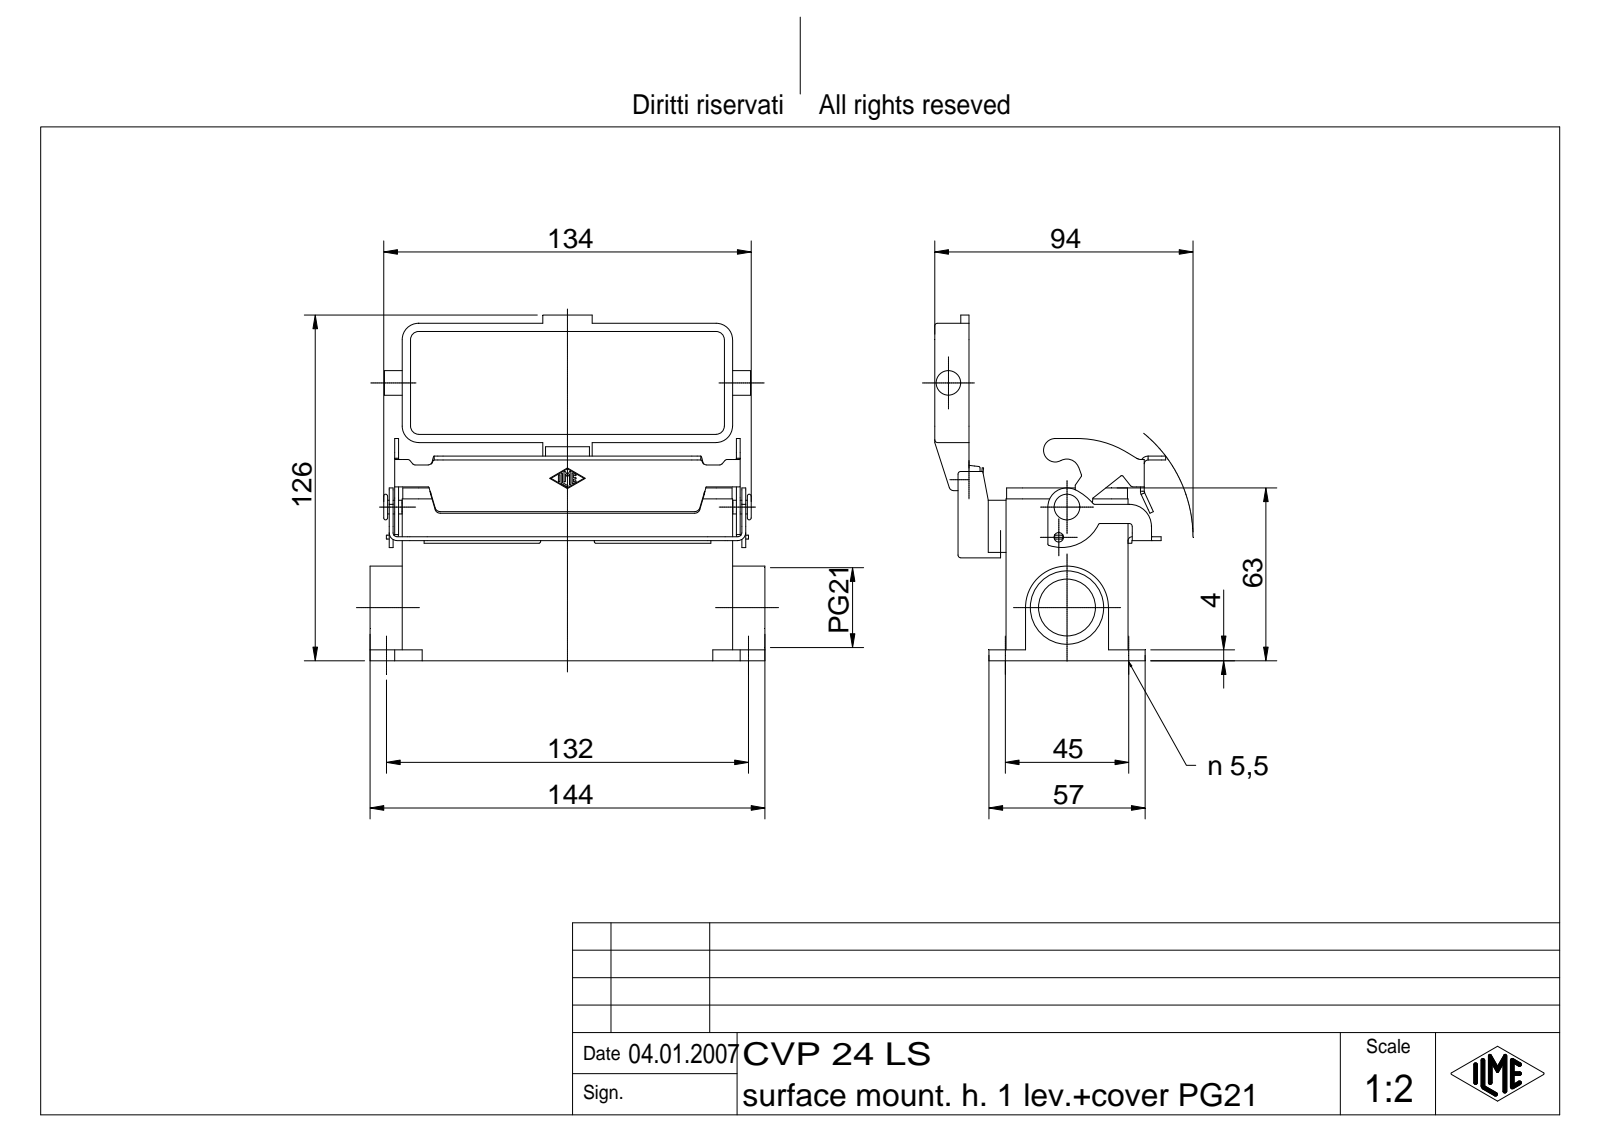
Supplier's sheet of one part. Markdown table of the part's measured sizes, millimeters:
| quantity | value |
| --- | --- |
| part name | CVP 24 LS |
| STEP written by | Autodesk Inventor 7 (AUTOMOTIVE_DESIGN) |
| units | millimeters |
| bodies | 4 solids, 572 faces (222 planar, 185 cylindrical, 165 other) |
| overall size | 144 × 126 × 84.23 |
| volume | 160 346 mm³ |
| surface area | 93 832 mm² |
| round holes (diameter × count) | 5.5 × 4, 3.5 × 1, 4 × 1, 20.78 × 1, 26.78 × 1 |
| round bosses / shafts (diameter × count) | 5 × 2, 9 × 1, 7 × 1, 3.2 × 1, 3 × 1 |
| partial cylindrical surfaces (radius × count) | 1 × 27, 0.25 × 15, 0.5 × 10, 1.5 × 10, 6 × 8, 2 × 7, 1.4 × 6, 2.8 × 6 |
| main face-to-face distances | 4, 40.5, 44.5, 36.5, 30, 23.5, 70.5, 66.5, 26, 2.5 |
| hole center spacings | 45, 132, 139.46, 25.79 |
